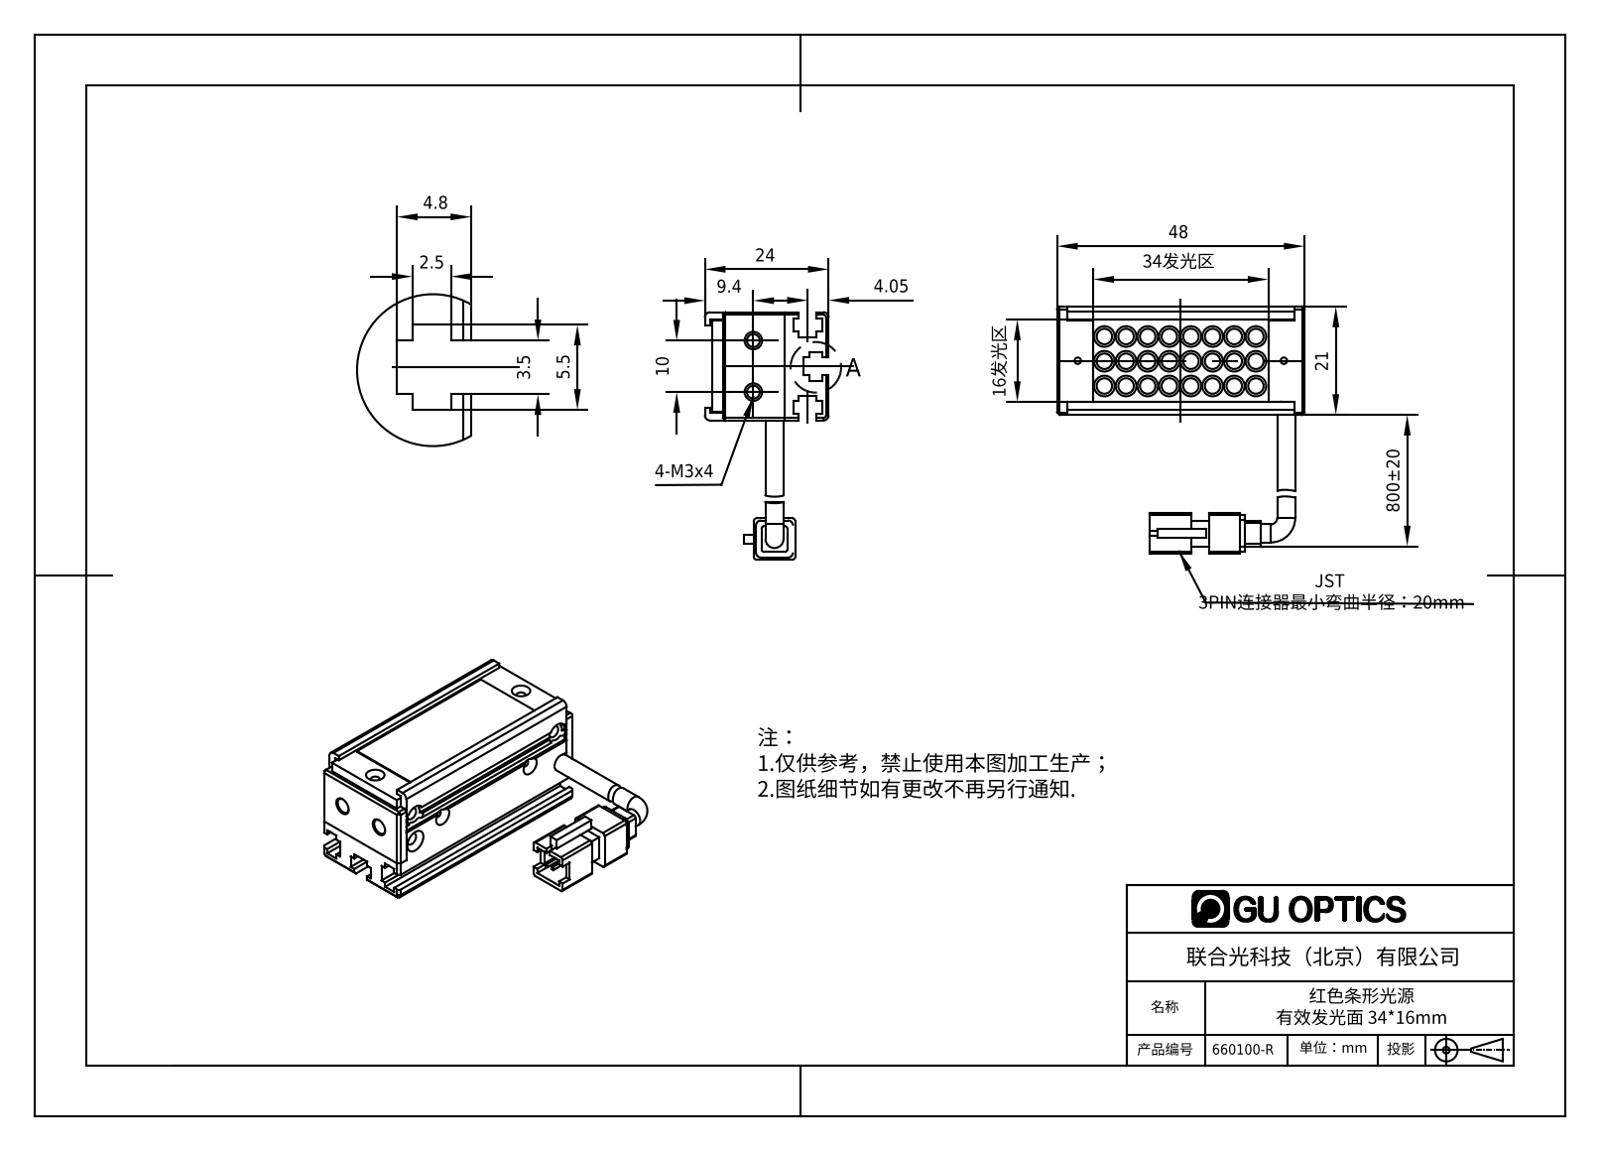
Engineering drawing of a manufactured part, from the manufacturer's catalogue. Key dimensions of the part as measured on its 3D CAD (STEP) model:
Part name (STEP PRODUCT): 660100-R
STEP written by: SolidWorks 2016 (AUTOMOTIVE_DESIGN)
Units: millimetres
Bodies: 6 solids, 878 faces (536 planar, 193 cylindrical, 149 other)
Overall size (bounding box): 48 × 48 × 24
Volume: 15 504 mm³ · Surface area: 16 054 mm²
Round holes (diameter × count): ⌀1.25 ×4, ⌀1.6 ×4, ⌀2.4 ×4, ⌀1.7 ×2, ⌀2.5 ×2, ⌀3 ×2, ⌀2 ×1
Round bosses / shafts (diameter × count): ⌀4 ×24, ⌀3 ×24, ⌀3.5 ×2
Partial cylindrical surfaces — rounded edges, fillets, slot ends (radius × count): R1 ×12, R0.5 ×8, R0.99 ×4, R1.65 ×1
Main face-to-face distances: 1, 2.5, 2, 18.5, 20.5, 1.3, 3.5, 12, 8.5, 15.7
Hole centre spacings: 6, 7.79, 8.45, 31.57, 31.74, 39, 39.46, 10
